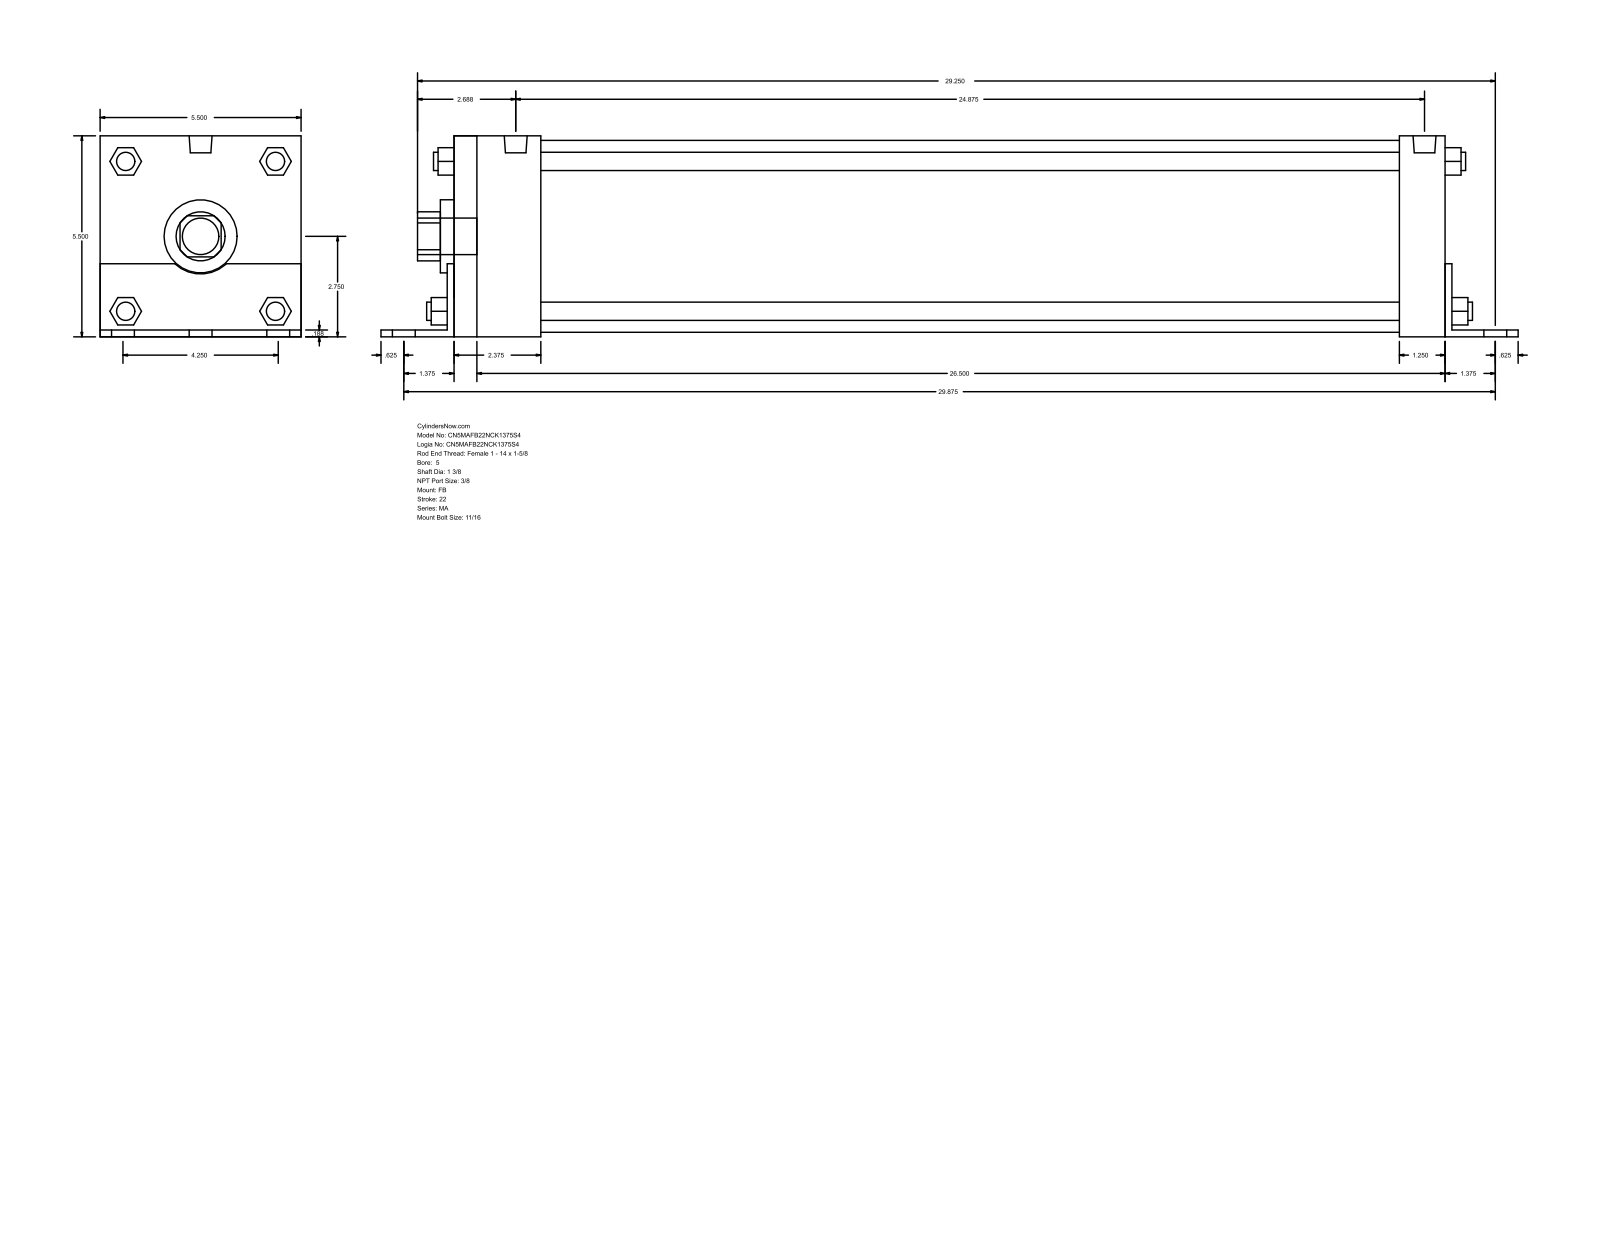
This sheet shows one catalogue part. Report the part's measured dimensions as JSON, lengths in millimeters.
{"part_name": "MA_FB__0500_1.375", "step_written_by": "GSSL Pune (CONFIG_CONTROL_DESIGN)", "units": "millimeters", "bodies": {"solids": 0, "faces": 140, "planar": 105, "cylindrical": 35, "other": 0}, "overall_size": [790.58, 139.75, 139.7], "round_holes": [[34.92, 1], [50.8, 1], [133.35, 1]], "round_bosses_or_shafts": [[17.46, 6], [12.7, 4], [11.11, 4], [15.93, 2], [25.4, 1]], "partial_cylinders_radius": [[17.06, 1], [26.16, 1]], "face_to_face_distances": [139.7, 4.76, 139.75, 693.74, 4.71, 134.99, 688.98, 698.5, 65.08, 60.32]}
